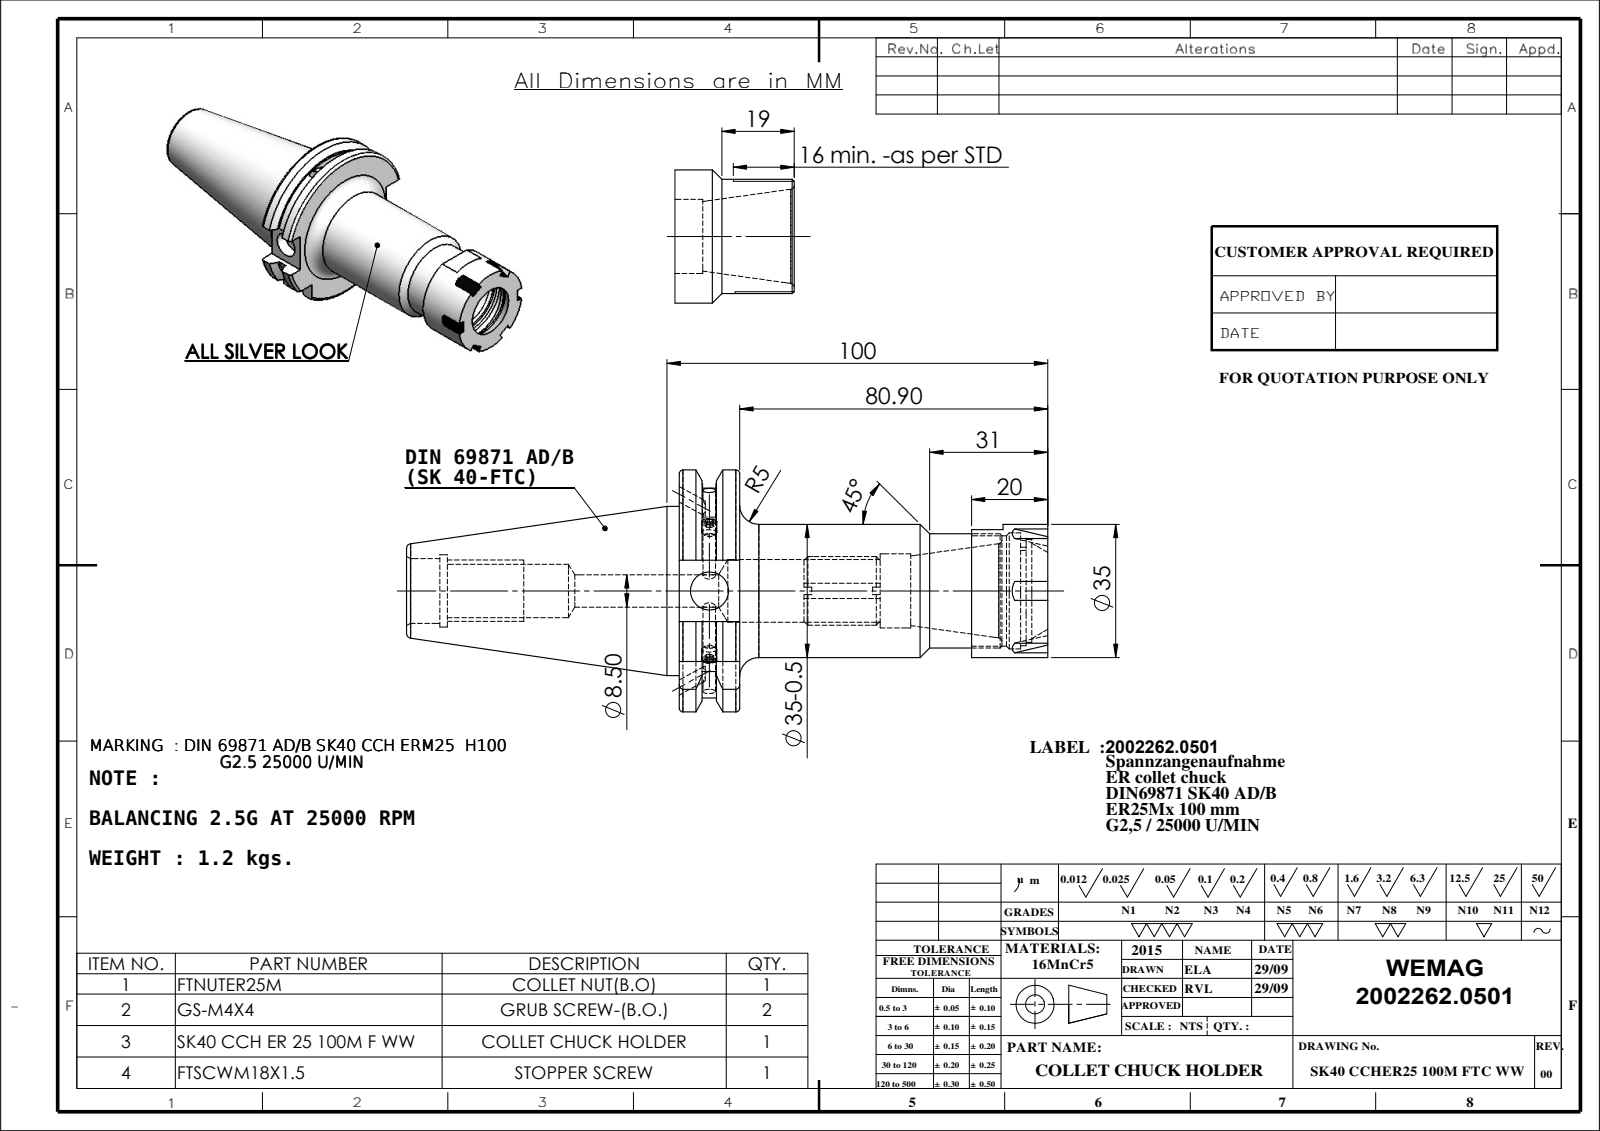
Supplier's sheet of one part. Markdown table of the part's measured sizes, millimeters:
| quantity | value |
| --- | --- |
| part name | SK40 CCH ER 25 100M F WW; FTNUTER25M; M4X4_DIN 913 - M4 x 4-N; FTSCWM18X150 (+1 more) |
| STEP written by | SolidWorks 2009 (CONFIG_CONTROL_DESIGN) |
| units | millimeters |
| bodies | 5 solids, 202 faces (90 planar, 56 cylindrical, 56 other) |
| overall size | 168.4 × 63.55 × 61.48 |
| volume | 155 969 mm³ |
| surface area | 38 885 mm² |
| round holes (diameter × count) | 3.3 × 1, 4 × 1, 8.5 × 1, 10 × 1, 14 × 1, 16.5 × 1, 17 × 1, 19 × 1, 19.5 × 1, 25.8 × 1, 27 × 1, 29 × 1 |
| round bosses / shafts (diameter × count) | 4 × 2, 44.45 × 1, 35 × 1, 30 × 1, 18 × 1 |
| partial cylindrical surfaces (radius × count) | 11.5 × 1, 28.12 × 1, 31.77 × 1 |
| main face-to-face distances | 15.9, 96.8, 80.9, 36.9, 20, 60.9, 76.8, 44, 24, 52.8 |
| hole center spacings | 1.5 |
